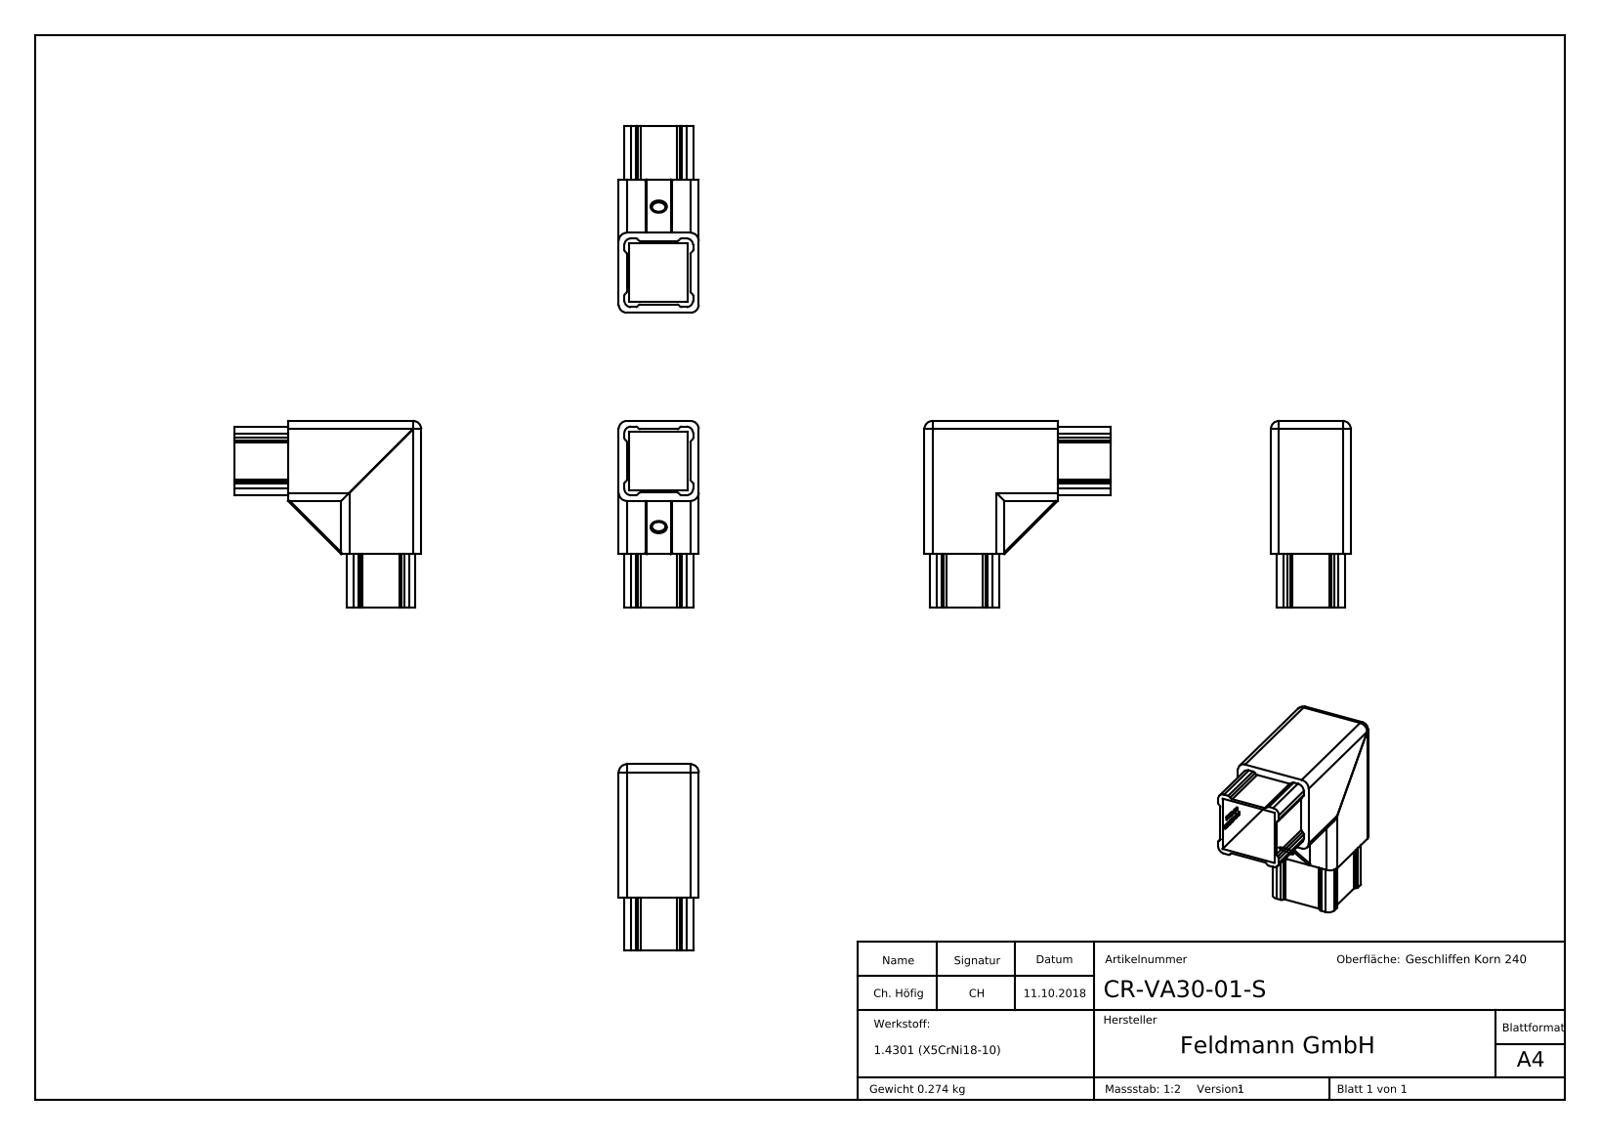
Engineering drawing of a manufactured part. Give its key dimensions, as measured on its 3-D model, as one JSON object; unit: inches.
{"part_name": "CR-VA30-01-S", "step_written_by": "SolidWorks 2015 (CONFIG_CONTROL_DESIGN)", "units": "inches", "bodies": {"solids": 1, "faces": 349, "planar": 185, "cylindrical": 51, "other": 113}, "overall_size": [2.756, 2.756, 1.181], "volume_in3": 2.118, "surface_area_in2": 35.78, "round_holes": [[0.197, 1]], "partial_cylinders_radius": [[0.039, 32], [0.118, 9], [0.098, 8]], "face_to_face_distances": [0.157, 1.024, 0.866, 1.181, 0.035, 0.122, 1.059, 0.902, 0.787, 0.937]}
